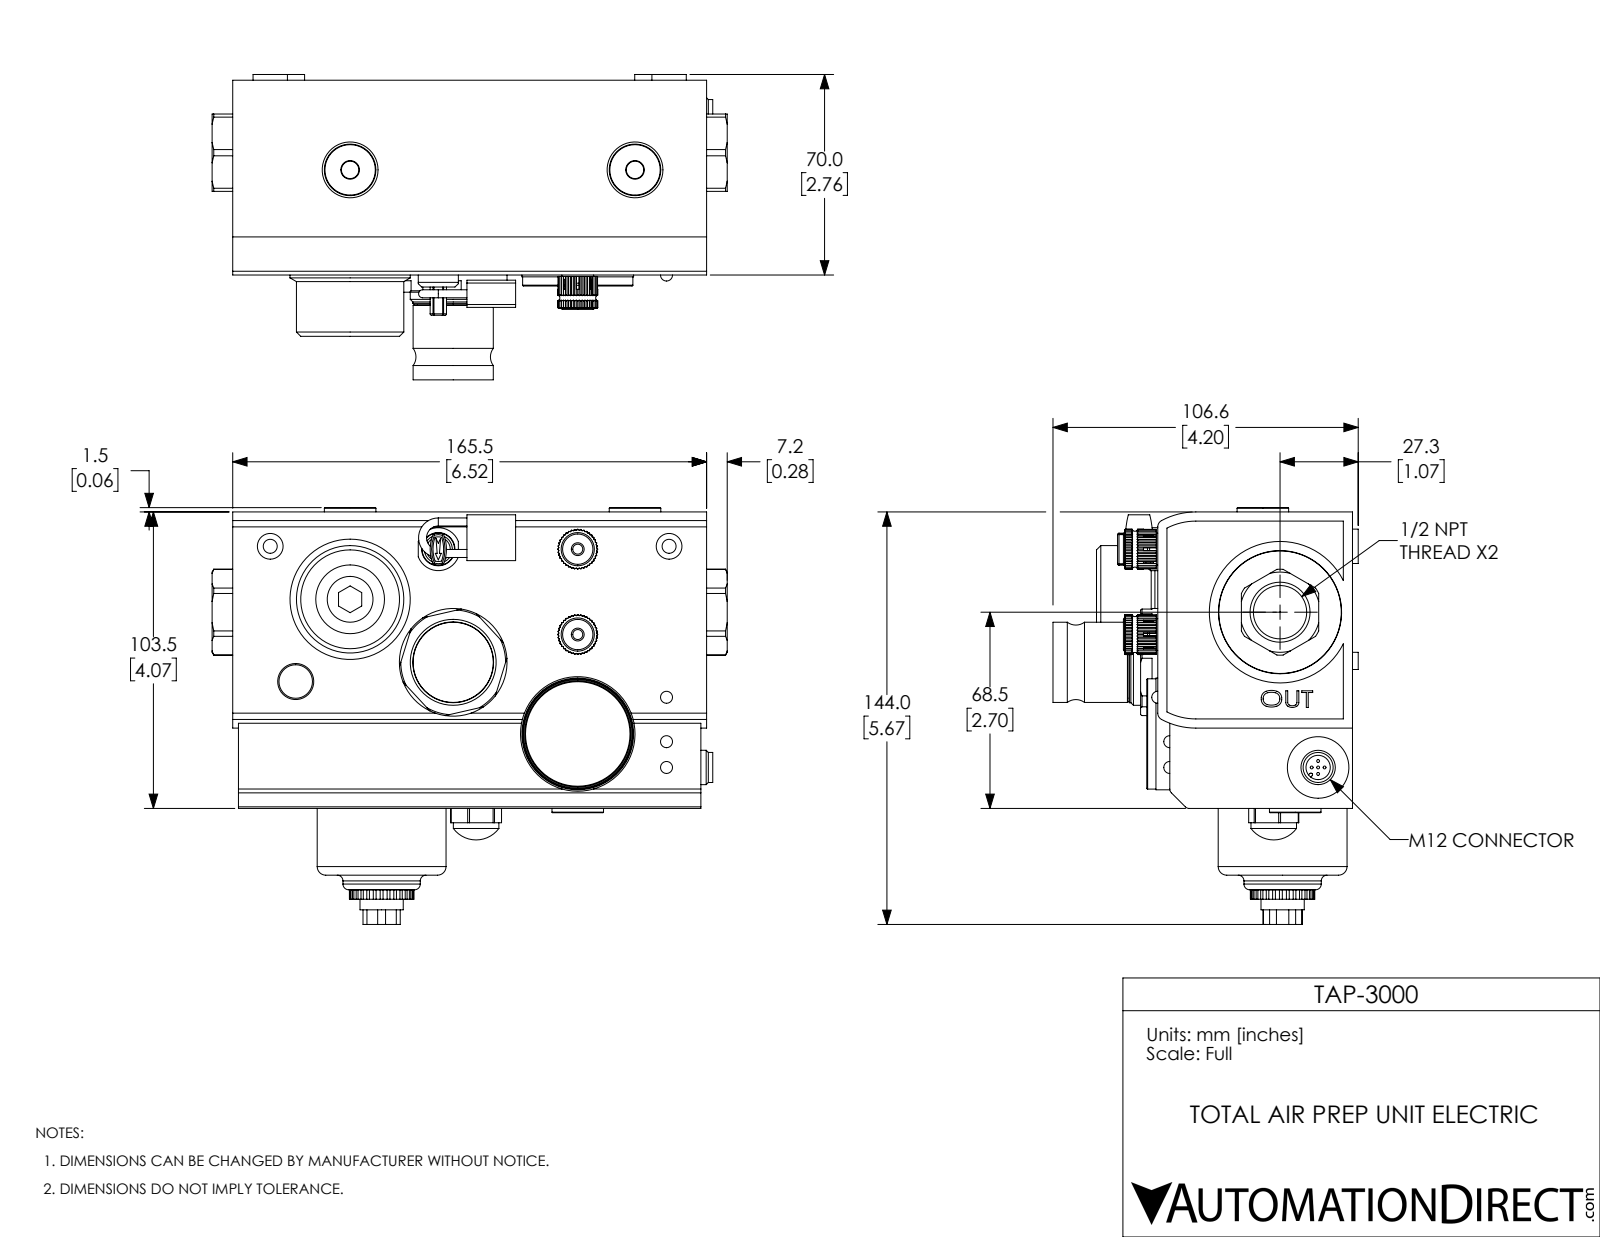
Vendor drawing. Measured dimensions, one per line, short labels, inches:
name: TAP-3000
written by: SolidWorks 2017 (AUTOMOTIVE_DESIGN)
unit: in
bodies: 10 solids, 1366 faces (737 planar, 355 cylindrical, 274 other)
size: 7.083 × 5.728 × 4.197
volume: 74.1 in³; area: 176.5 in²
holes: 3× ⌀0.24, 3× ⌀0.768, 2× ⌀0.098, 2× ⌀0.193, 2× ⌀0.256, 2× ⌀0.354, 2× ⌀0.433, 2× ⌀0.518, 1× ⌀0.189, 1× ⌀0.335, 1× ⌀0.337, 1× ⌀0.449
bosses: 5× ⌀0.437, 5× ⌀0.039, 3× ⌀0.709, 3× ⌀0.472, 2× ⌀0.335, 2× ⌀0.309, 2× ⌀0.276, 2× ⌀0.236
rounds: 29× R0.071, 6× R0.02, 6× R0.098, 4× R0.079, 4× R0.229, 4× R0.282, 2× R0.039, 2× R0.059
face distances: 2.677, 4.075, 0.039, 0.047, 6.35, 0.087, 6.39, 6.303, 0.126, 6.437
hole spacings: 1.614, 5.366, 0.283, 0.511, 0.73, 0.904, 0.972, 1.127
